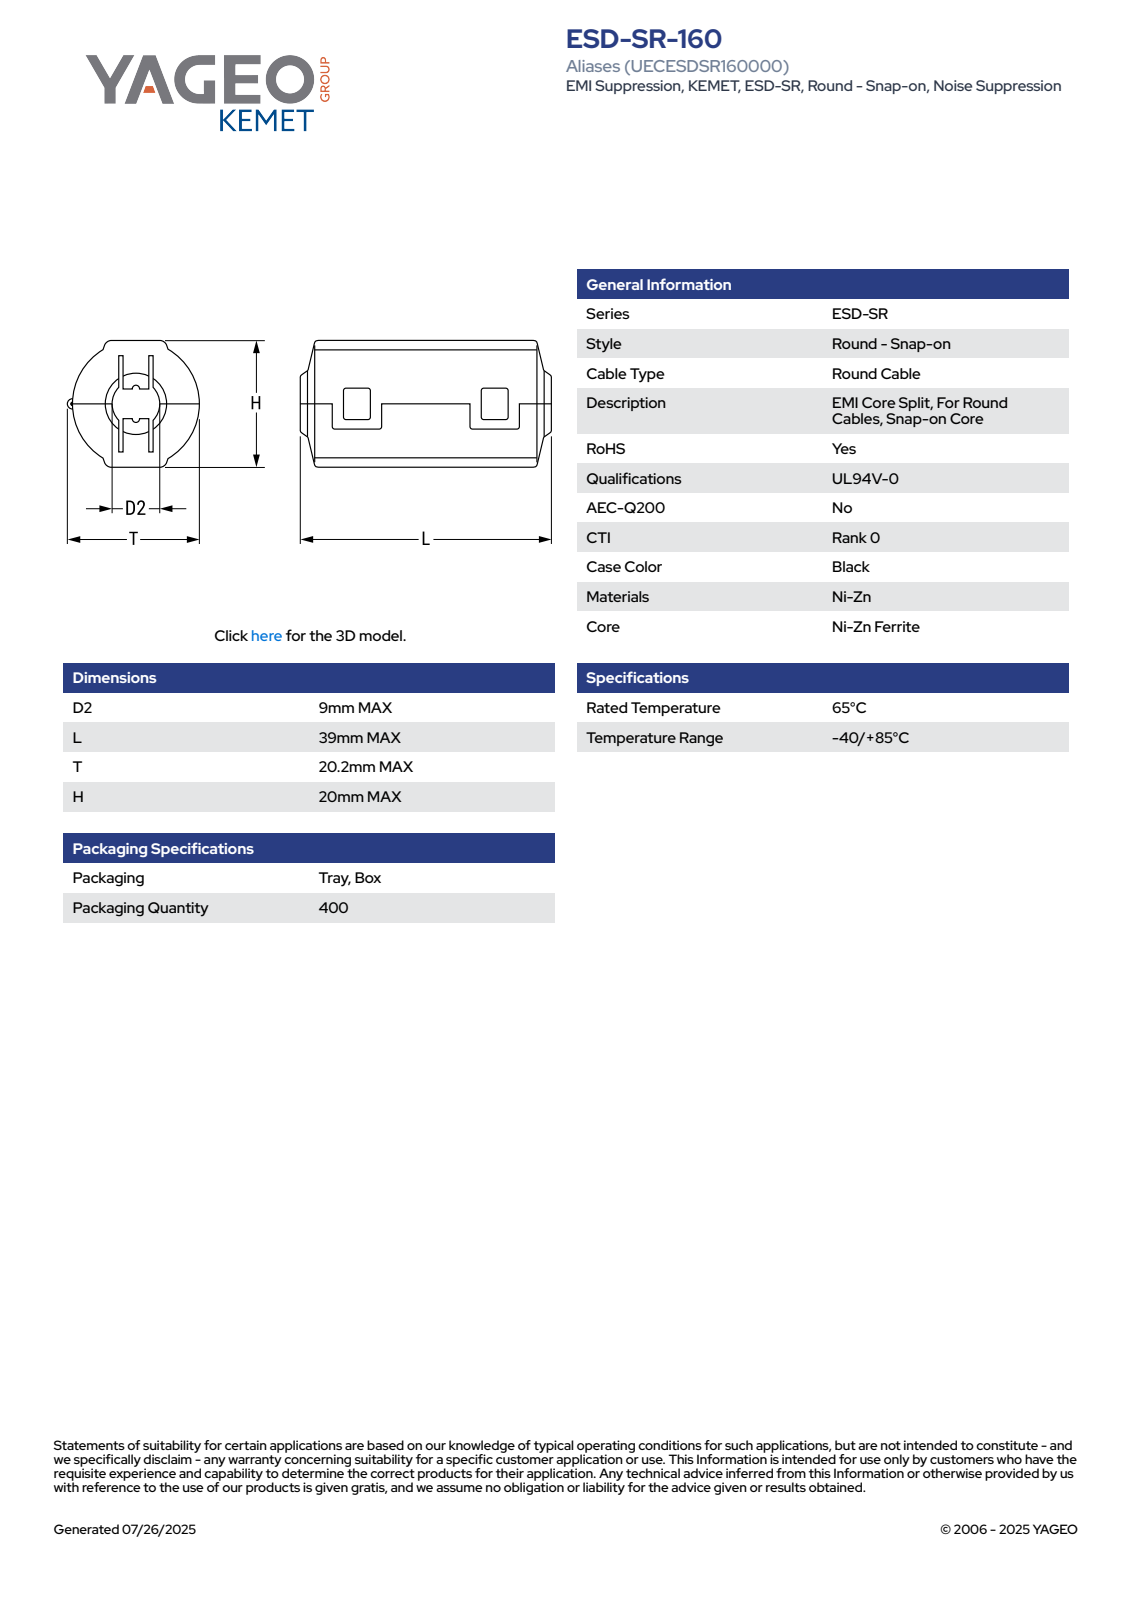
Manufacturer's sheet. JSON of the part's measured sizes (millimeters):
{"part_name": "EC_ESDSR_D29L39T20.2H20", "step_written_by": "SolidWorks 2014 (AUTOMOTIVE_DESIGN)", "units": "millimeters", "bodies": {"solids": 1, "faces": 92, "planar": 72, "cylindrical": 6, "other": 14}, "overall_size": [39, 20.2, 20], "volume_mm3": 10692, "surface_area_mm2": 4020, "partial_cylinders_radius": [[3.39, 2], [10.1, 1]], "face_to_face_distances": [7.44, 12.56, 20, 5.12, 12.76, 2.25, 36.75, 39, 34.5, 4.2]}
